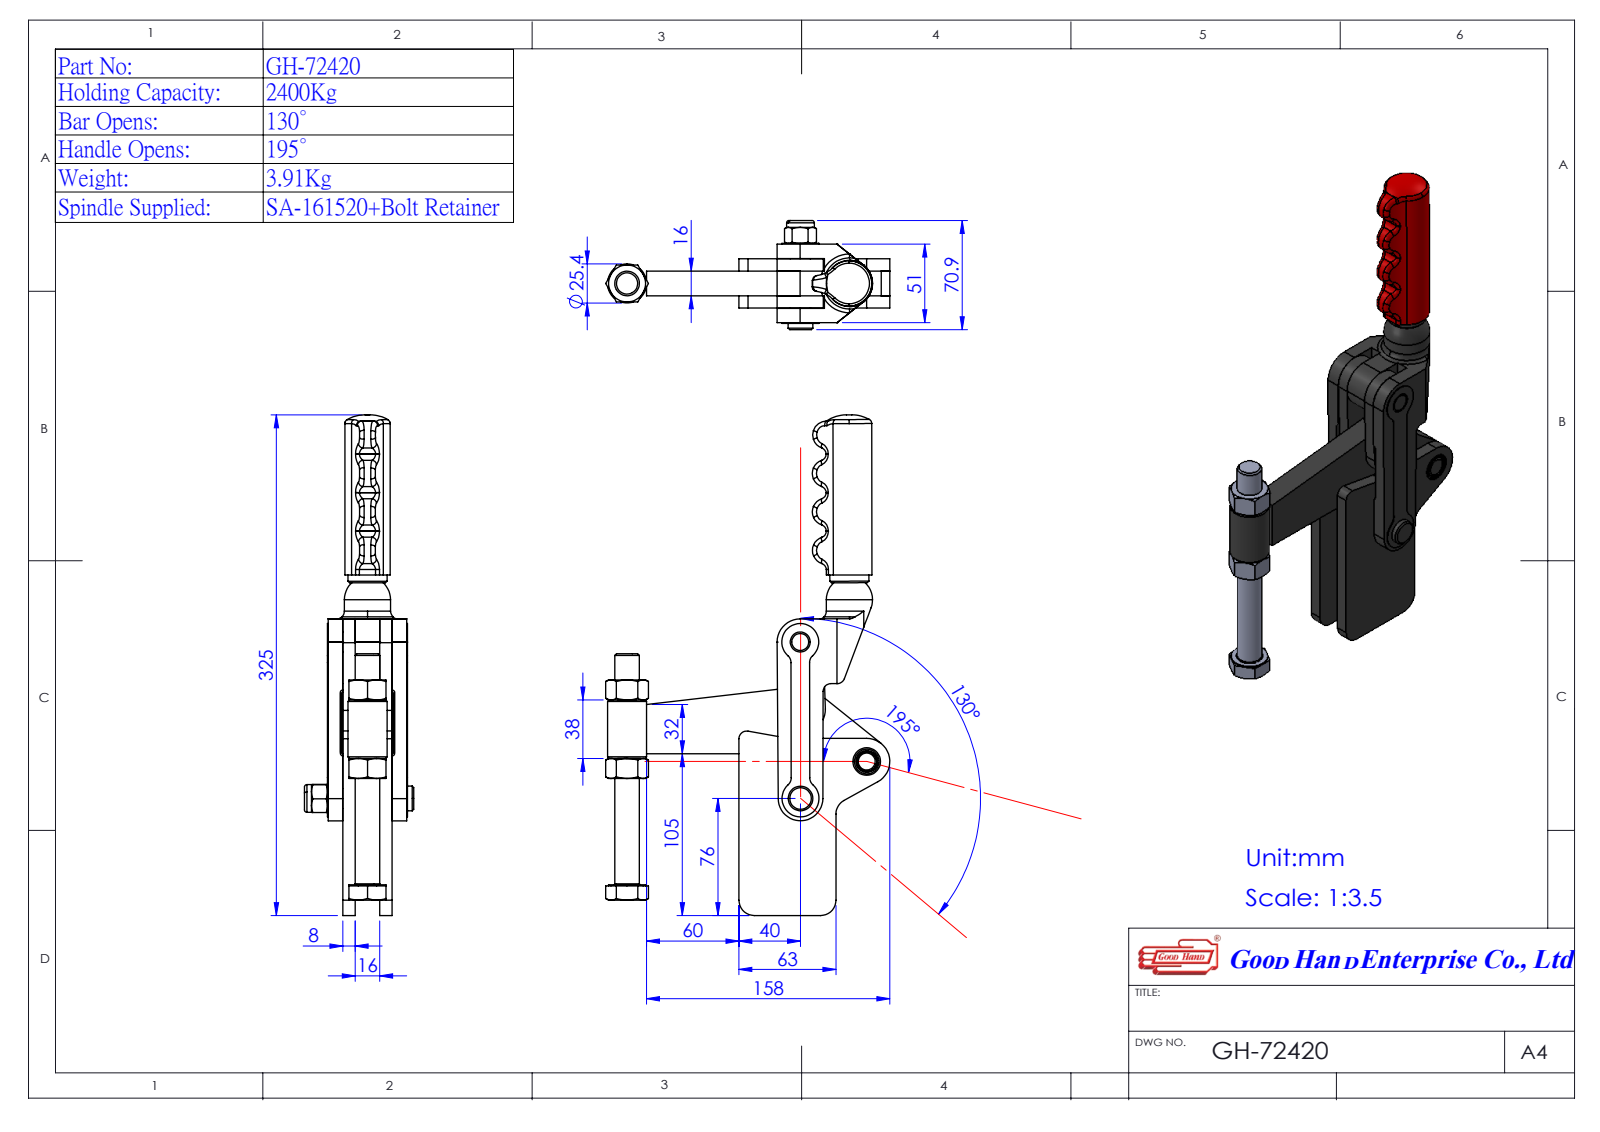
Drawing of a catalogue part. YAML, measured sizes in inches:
part_name: "Group2^GH-72420(簡化); Group1^GH-72420(簡化); GH-72420(簡化); Continuous Thread Hexagon Head Bolt_A_JIS-1^GH-72420(簡化) (+3 more)"
step_written_by: "SolidWorks 2016 (AUTOMOTIVE_DESIGN)"
units: inches
bodies: {solids: 6, faces: 283, planar: 121, cylindrical: 103, other: 59}
overall_size: [12.798, 7.458, 2.613]
volume: 33.1
surface_area: 208.2
round_holes:
  - {diameter: 0.354, count: 4}
  - {diameter: 0.63, count: 1}
round_bosses_or_shafts:
  - {diameter: 1, count: 2}
  - {diameter: 1.181, count: 1}
  - {diameter: 0.945, count: 1}
  - {diameter: 0.63, count: 1}
  - {diameter: 0.591, count: 1}
partial_cylinders:
  - {radius: 0.161, count: 7}
  - {radius: 0.591, count: 5}
  - {radius: 0.236, count: 4}
  - {radius: 0.354, count: 4}
  - {radius: 0.197, count: 3}
  - {radius: 0.394, count: 3}
  - {radius: 0.472, count: 2}
  - {radius: 0.709, count: 2}
face_to_face_distances: [0.945, 0.315, 0.63, 1.26, 0.321, 0.951, 1.266, 0.368, 0.374, 0.689]
hole_center_spacings: [1.732, 1.939, 2.113, 2.269, 3.496, 4]
